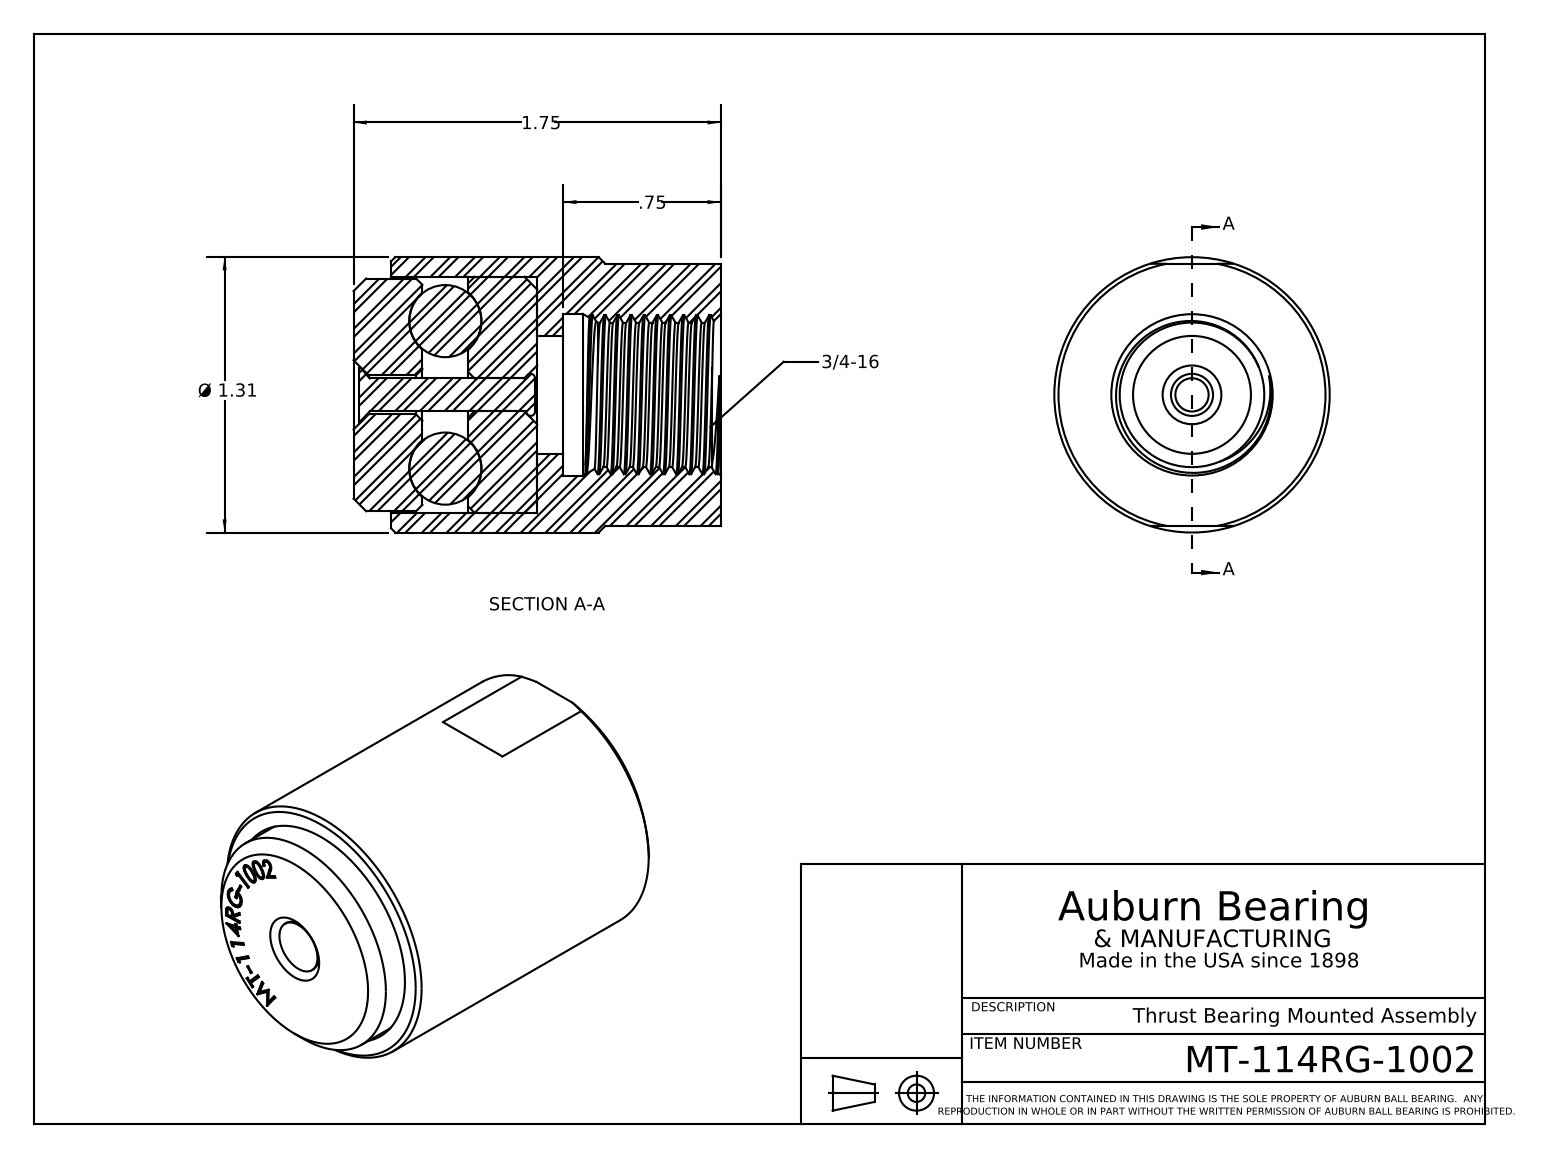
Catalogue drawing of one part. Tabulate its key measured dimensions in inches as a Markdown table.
| quantity | value |
| --- | --- |
| part name | MT-114RG-1002 |
| STEP written by | SolidWorks 2020 (CONFIG_CONTROL_DESIGN) |
| units | inches |
| bodies | 10 solids, 245 faces (116 planar, 41 cylindrical, 88 other) |
| overall size | 1.75 × 1.313 × 1.313 |
| volume | 1.779 in³ |
| surface area | 22.84 in² |
| round holes (diameter × count) | 0.156 × 1, 0.187 × 1, 0.562 × 1, 0.689 × 1, 0.77 × 1, 1.124 × 1, 1.128 × 1 |
| round bosses / shafts (diameter × count) | 1.313 × 1, 1.125 × 1, 1.109 × 1, 0.256 × 1 |
| main face-to-face distances | 0.875, 0.875, 1.75, 0.328, 0.547, 0.179, 0.696, 1.571, 0.368, 1.203 |
